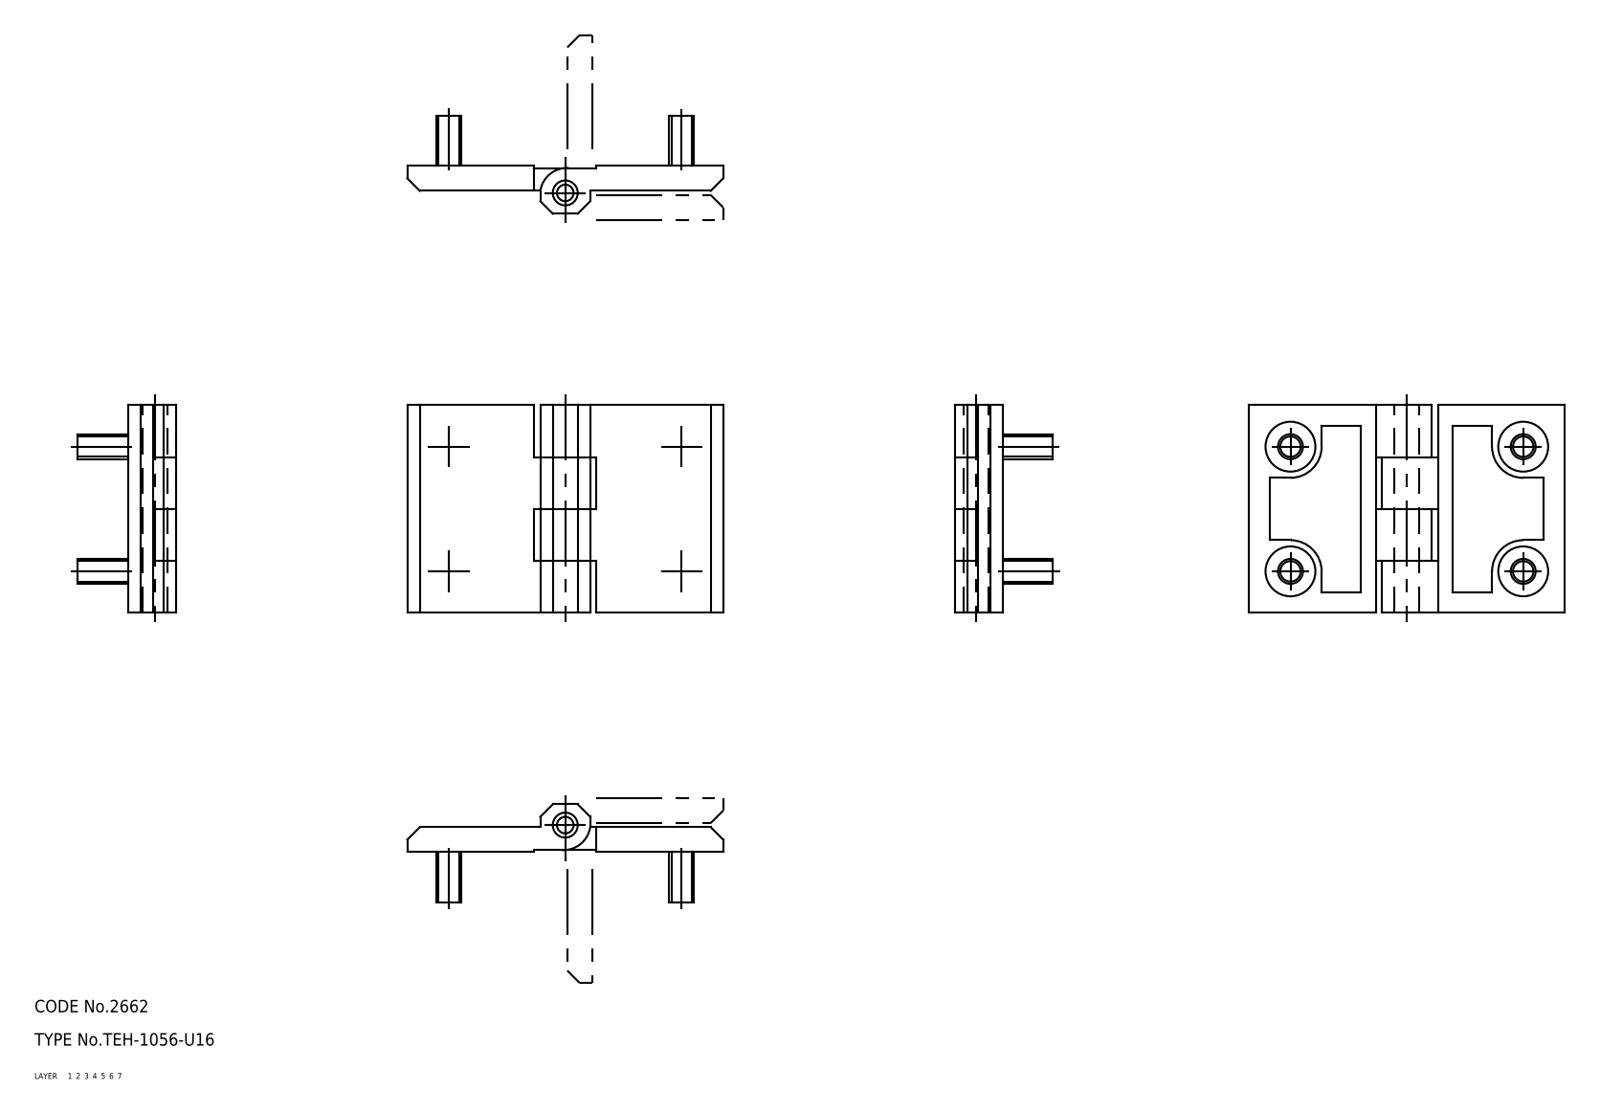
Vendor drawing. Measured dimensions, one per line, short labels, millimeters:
name: screw; shaft; hinge pieces_B; hinge pieces_A (+1 more)
written by: CADfix (AUTOMOTIVE_DESIGN)
unit: mm
bodies: 7 solids, 114 faces (0 planar, 0 cylindrical, 114 other)
size: 76 × 50 × 23.5
volume: 21 261 mm³; area: 14 271 mm²
